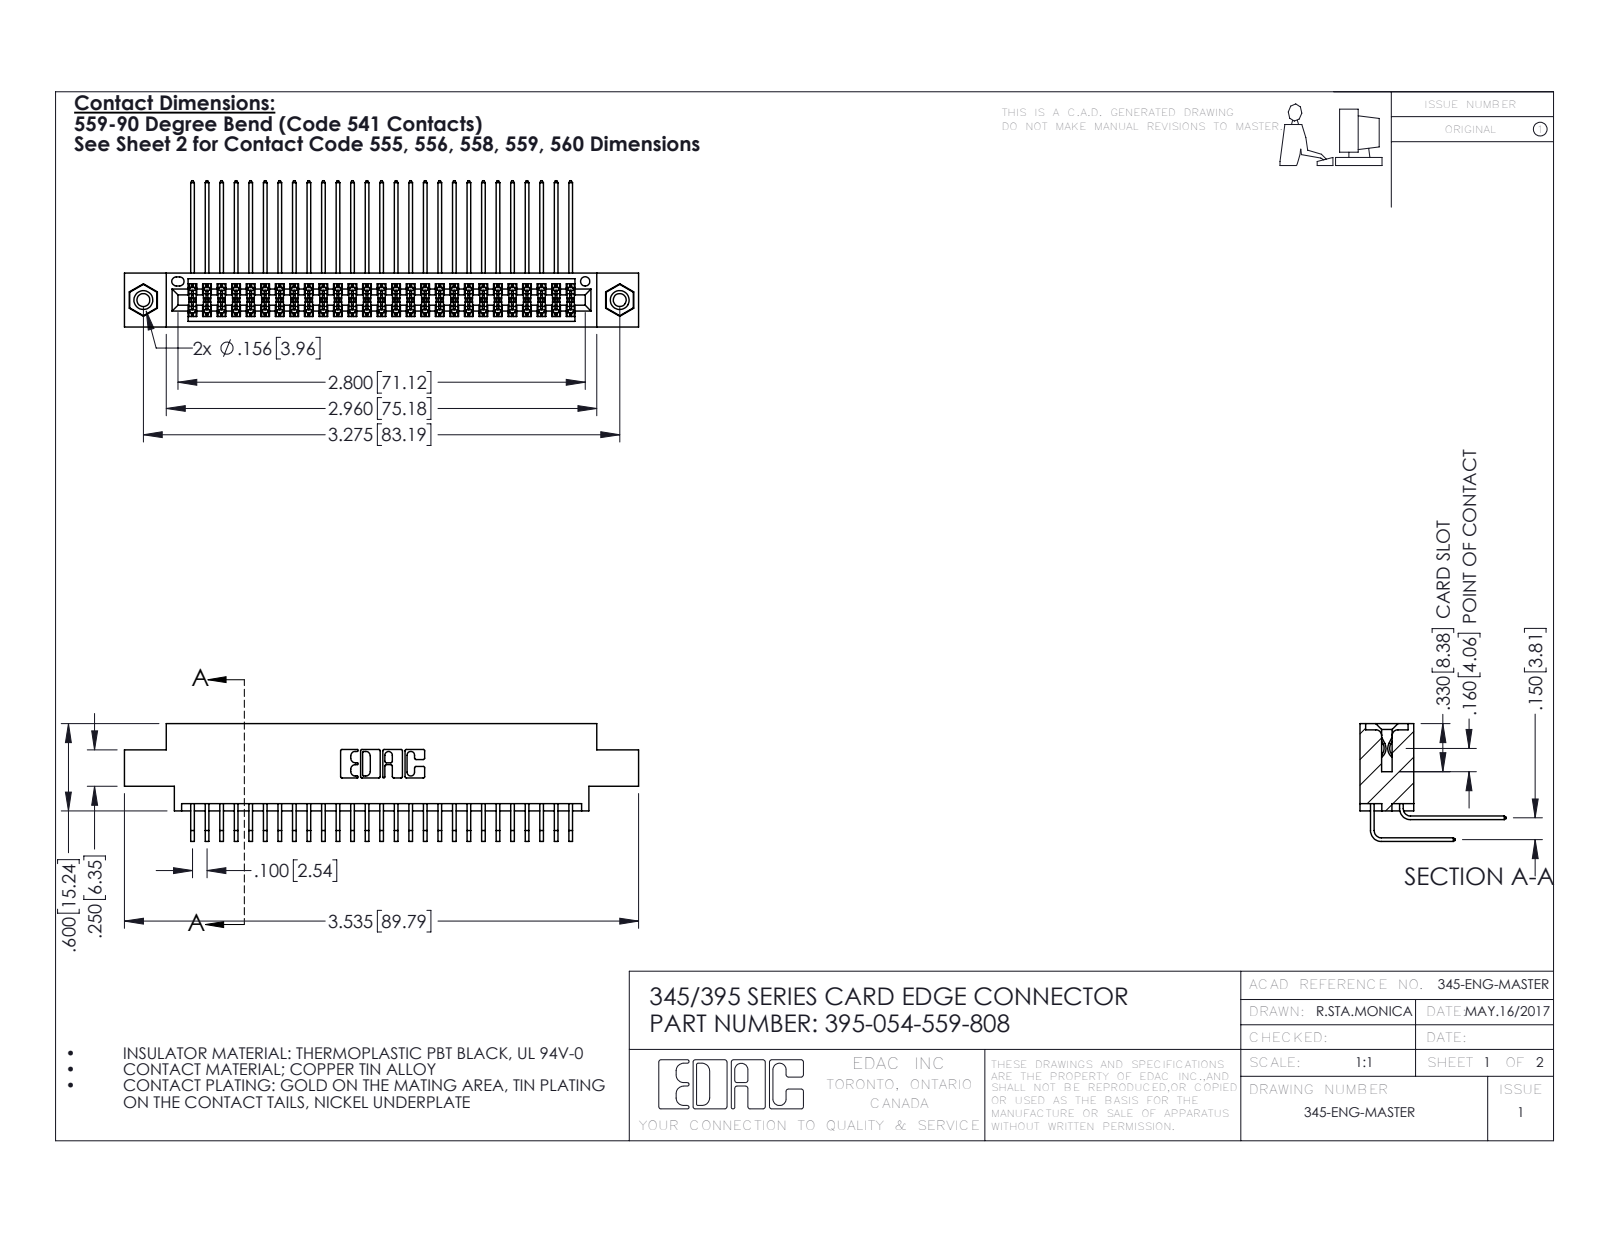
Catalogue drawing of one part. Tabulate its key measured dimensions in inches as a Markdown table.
| quantity | value |
| --- | --- |
| part name | 345 Part_0.170 Offset - 0.156 Dia-TI; 345-292-001_559 Tail - 2; 345-292-001_558 559 Tail - 1; 395-054-559-808 (+1 more) |
| STEP written by | SolidWorks 2016 (CONFIG_CONTROL_DESIGN) |
| units | inches |
| bodies | 57 solids, 2998 faces (2006 planar, 976 cylindrical, 16 other) |
| overall size | 3.535 × 1.005 × 0.809 |
| volume | 0.535 in³ |
| surface area | 22.17 in² |
| round holes (diameter × count) | 0.089 × 2, 0.125 × 2, 0.156 × 2, 0.064 × 1 |
| round bosses / shafts (diameter × count) | 0.155 × 2 |
| partial cylindrical surfaces (radius × count) | 0.006 × 81, 0.01 × 22, 0.007 × 6, 0.031 × 6, 0.026 × 3, 0.014 × 2, 0.019 × 2, 0.022 × 2 |
| main face-to-face distances | 0.072, 0.298, 0.37, 0.2, 0.098, 0.272, 0.025, 0.225, 0.175, 0.15 |
| hole center spacings | 0.27, 3.04, 3.275 |
